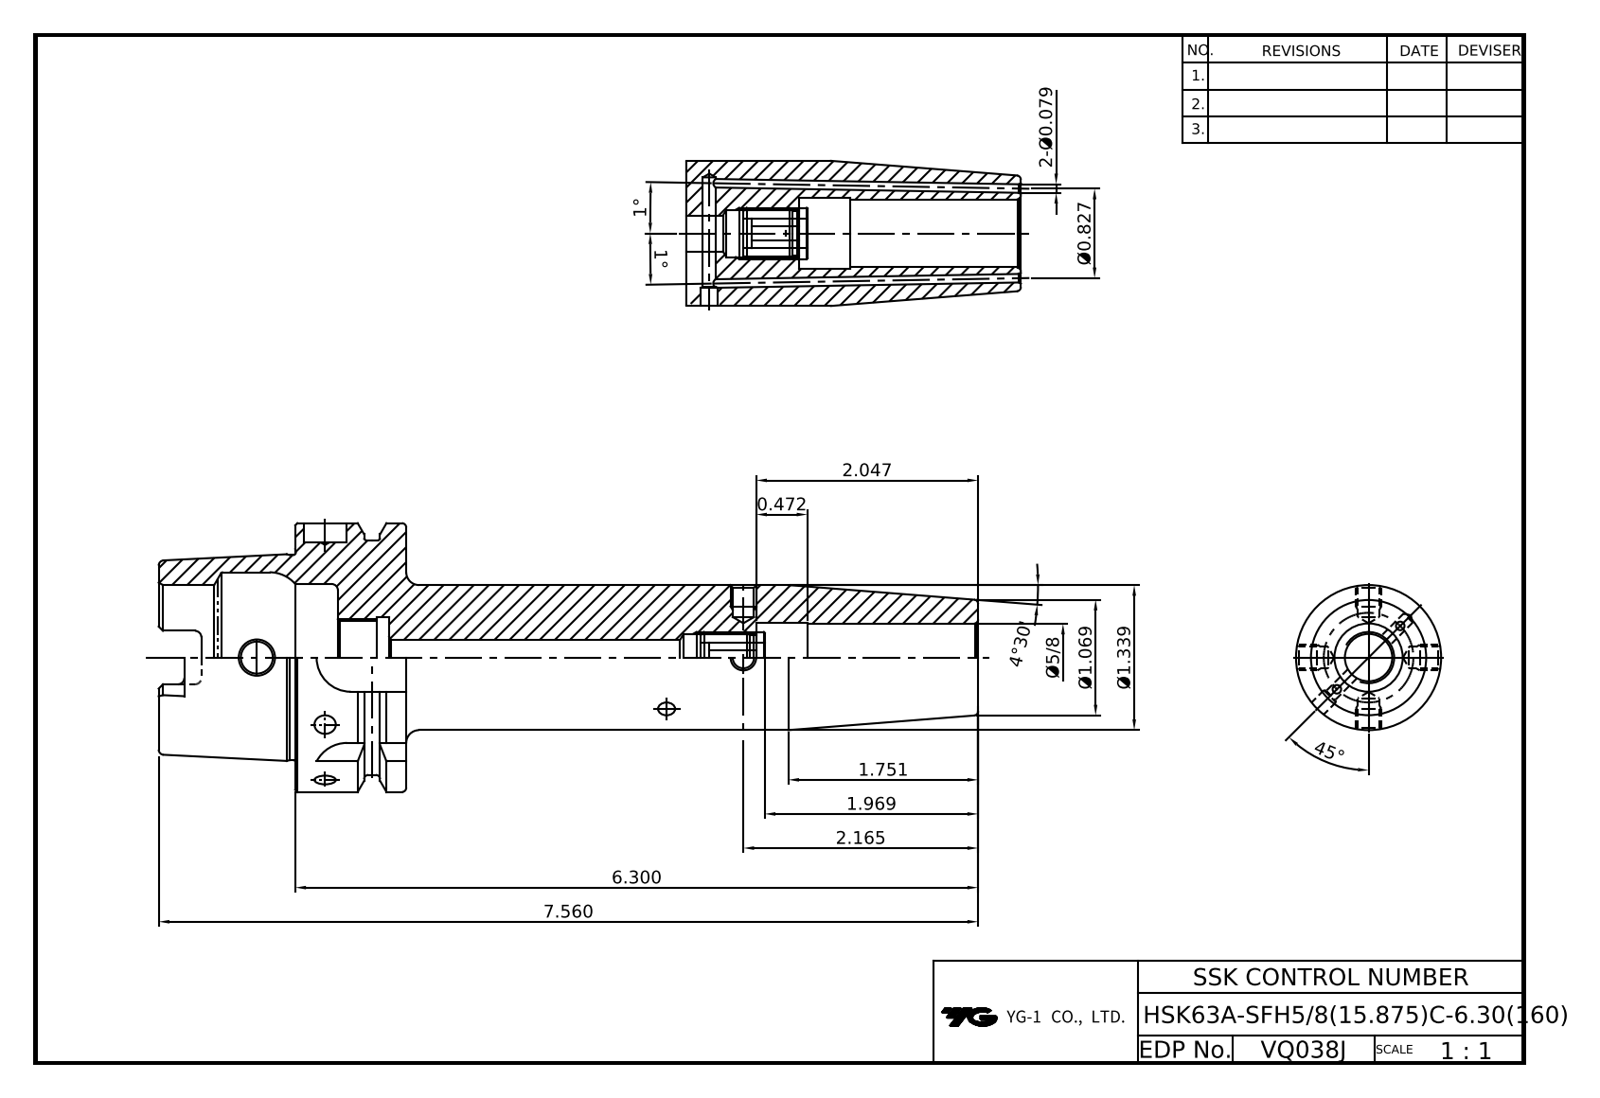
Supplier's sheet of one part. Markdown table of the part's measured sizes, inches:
| quantity | value |
| --- | --- |
| part name | HSK63A_BALANCE_20200217 |
| STEP written by | CREO PARAMETRIC BY PTC INC, 2018500 (CONFIG_CONTROL_DESIGN) |
| units | inches |
| bodies | 1 solid, 184 faces (57 planar, 57 cylindrical, 70 other) |
| overall size | 7.559 × 2.48 × 2.48 |
| volume | 10.94 in³ |
| surface area | 65.09 in² |
| round holes (diameter × count) | 0.197 × 2, 0.295 × 1, 0.331 × 1, 0.394 × 1, 0.433 × 1, 0.472 × 1, 0.625 × 1, 0.649 × 1, 0.669 × 1, 0.709 × 1, 0.748 × 1, 1.339 × 1 |
| round bosses / shafts (diameter × count) | 2.48 × 1, 2.165 × 1, 1.891 × 1 |
| partial cylindrical surfaces (radius × count) | 0.059 × 6, 0.113 × 4, 0.315 × 4 |
| main face-to-face distances | 1.024, 0.394, 0.63, 1.26, 0.241, 0.389, 1.654, 2.283, 0.157, 5.276 |
